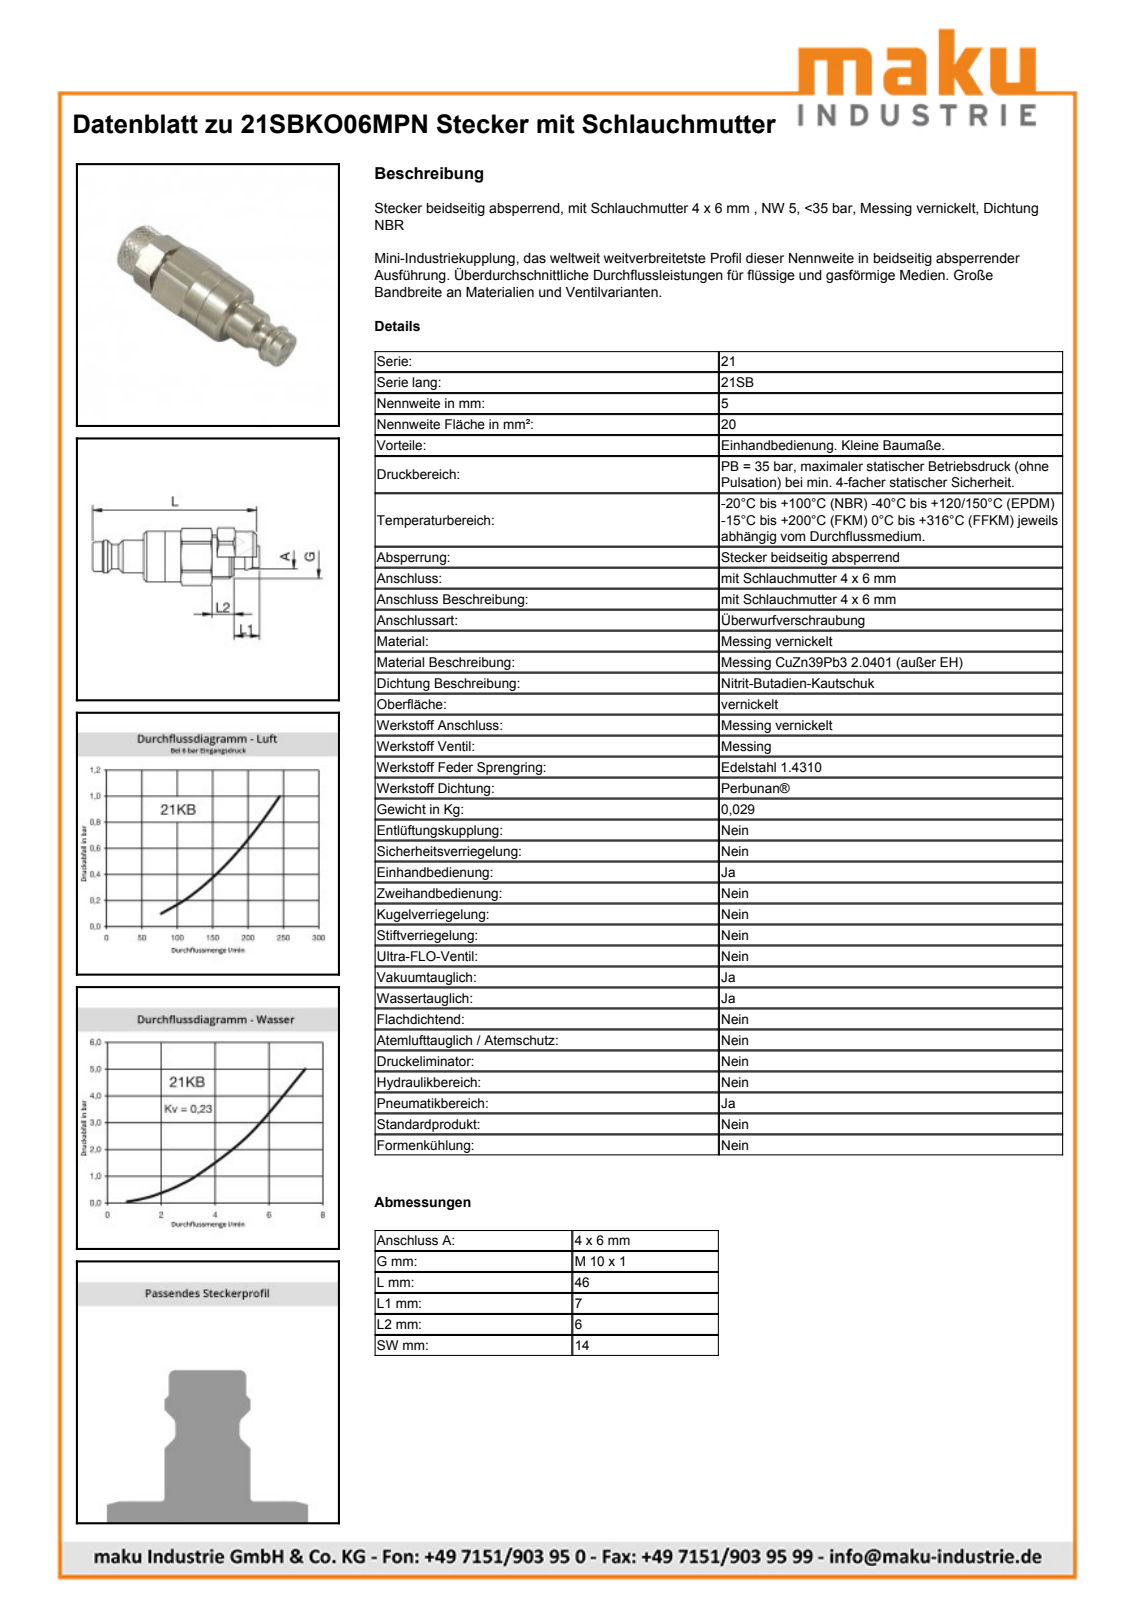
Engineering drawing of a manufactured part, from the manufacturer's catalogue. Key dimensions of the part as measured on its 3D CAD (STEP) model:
Part name (STEP PRODUCT): D105884
STEP written by: Autodesk Inventor 2011 (AUTOMOTIVE_DESIGN)
Units: millimetres
Bodies: 1 solid, 97 faces (22 planar, 28 cylindrical, 47 other)
Overall size (bounding box): 45.85 × 15.54 × 15.27
Volume: 4 895 mm³ · Surface area: 2 827 mm²
Round holes (diameter × count): ⌀6.2 ×1, ⌀8.92 ×1, ⌀12 ×1
Round bosses / shafts (diameter × count): ⌀14 ×1, ⌀11.98 ×1, ⌀11.05 ×1, ⌀10 ×1, ⌀9 ×1, ⌀8.6 ×1, ⌀8.1 ×1, ⌀6.65 ×1
Partial cylindrical surfaces — rounded edges, fillets, slot ends (radius × count): R6.75 ×1, R7.9 ×1
Main face-to-face distances: 14, 12, 12.1, 18.65, 30.75, 14.1, 32.75, 44.85, 38.85, 24.75
